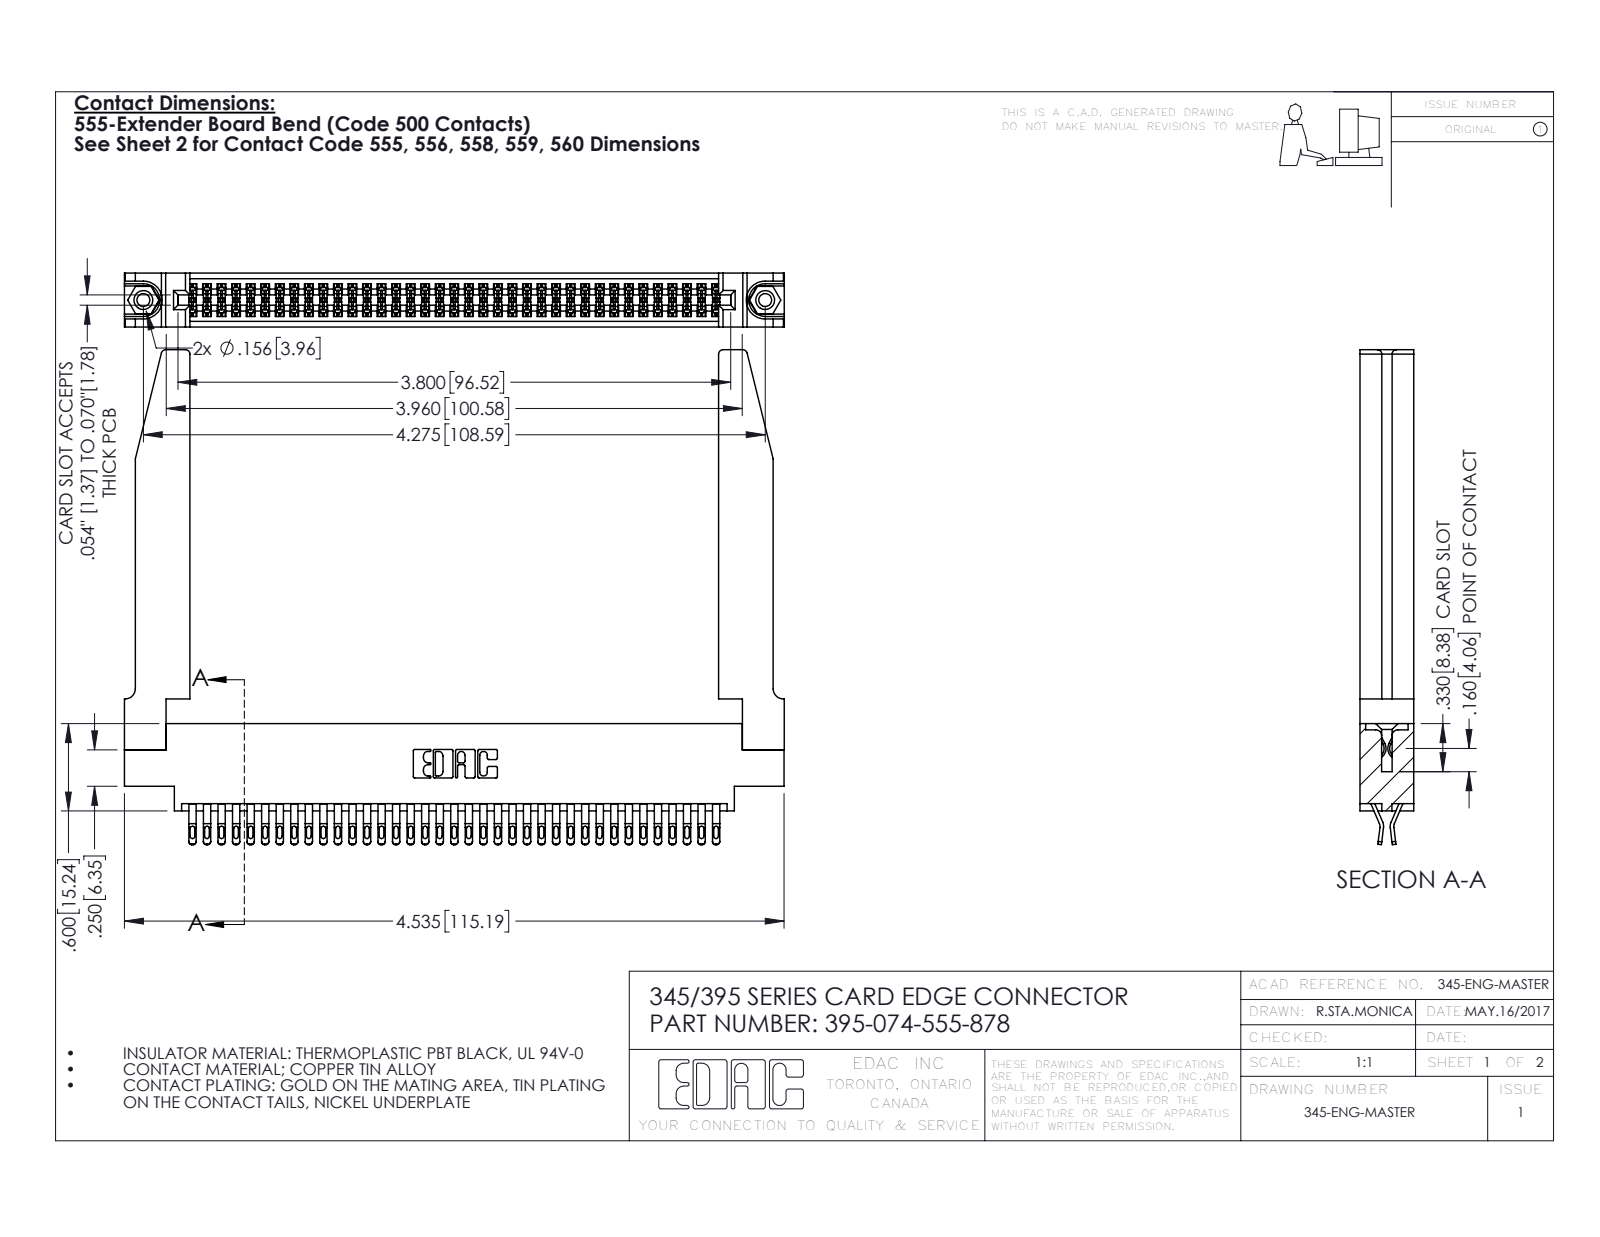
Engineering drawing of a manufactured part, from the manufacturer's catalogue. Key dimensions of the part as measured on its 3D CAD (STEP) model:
Part name (STEP PRODUCT): 345-250-001_345-250-001-102; 345-292-001_555 Tail; 345 Part_0.170 Offset - 0.156 Dia-TH; 345-220-078_345-220-078 (+1 more)
STEP written by: SolidWorks 2016 (CONFIG_CONTROL_DESIGN)
Units: inches
Bodies: 79 solids, 4508 faces (2520 planar, 1936 cylindrical, 52 other)
Overall size (bounding box): 4.536 × 3.402 × 0.37
Volume: 1.161 in³ · Surface area: 37.6 in²
Round holes (diameter × count): ⌀0.089 ×2, ⌀0.125 ×2, ⌀0.156 ×2, ⌀0.064 ×1
Round bosses / shafts (diameter × count): ⌀0.155 ×2
Partial cylindrical surfaces — rounded edges, fillets, slot ends (radius × count): R0.016 ×185, R0.02 ×148, R0.006 ×111, R0.01 ×22, R0.03 ×8, R0.007 ×6, R0.031 ×6, R0.026 ×3
Main face-to-face distances: 0.37, 0.072, 0.298, 0.025, 0.098, 0.272, 0.2, 0.225, 0.175, 0.15
Hole centre spacings: 0.27, 4.039, 4.275
